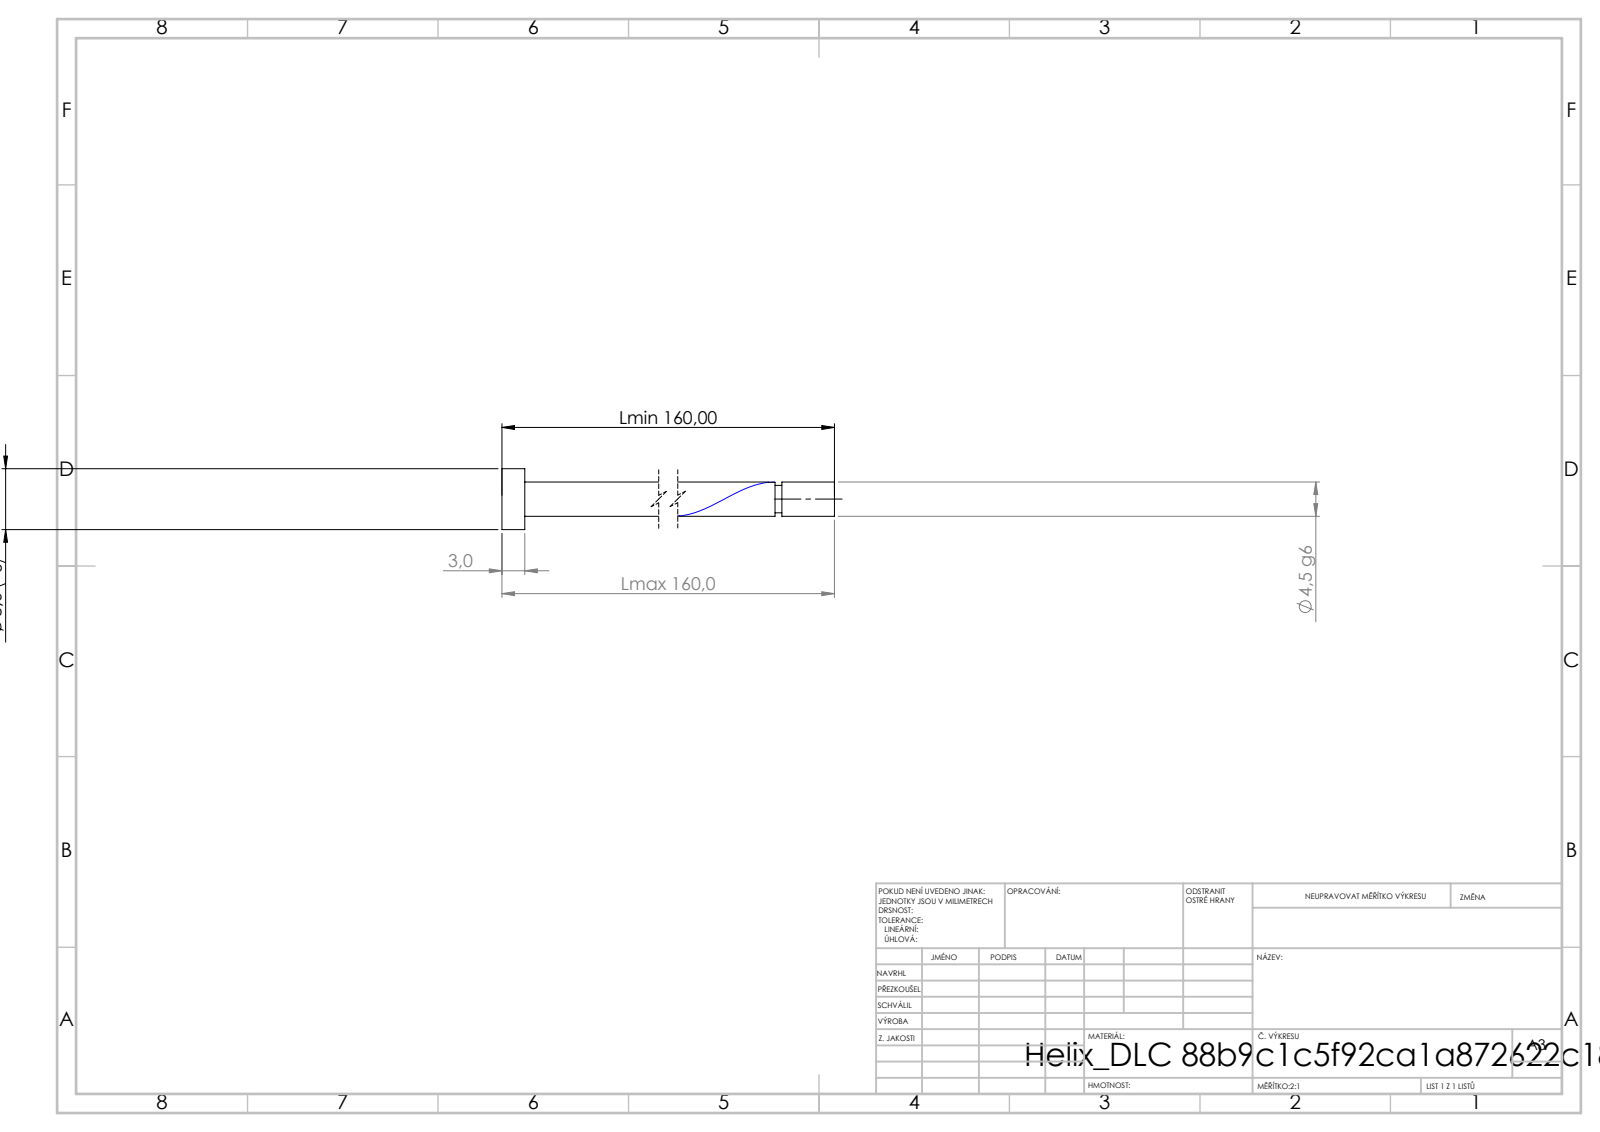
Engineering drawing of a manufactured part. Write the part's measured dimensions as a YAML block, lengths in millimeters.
step_written_by: "SolidWorks 2019 (CONFIG_CONTROL_DESIGN)"
units: millimeters
bodies: {solids: 1, faces: 21, planar: 6, cylindrical: 14, other: 1}
overall_size: [160, 8, 8]
volume: 2618
surface_area: 2445
round_bosses_or_shafts:
  - {diameter: 8, count: 1}
  - {diameter: 4.5, count: 1}
  - {diameter: 3.6, count: 1}
face_to_face_distances: [3, 160, 157, 153.1, 150.1, 6.9, 152.2, 149.2, 0.9, 7.8]
